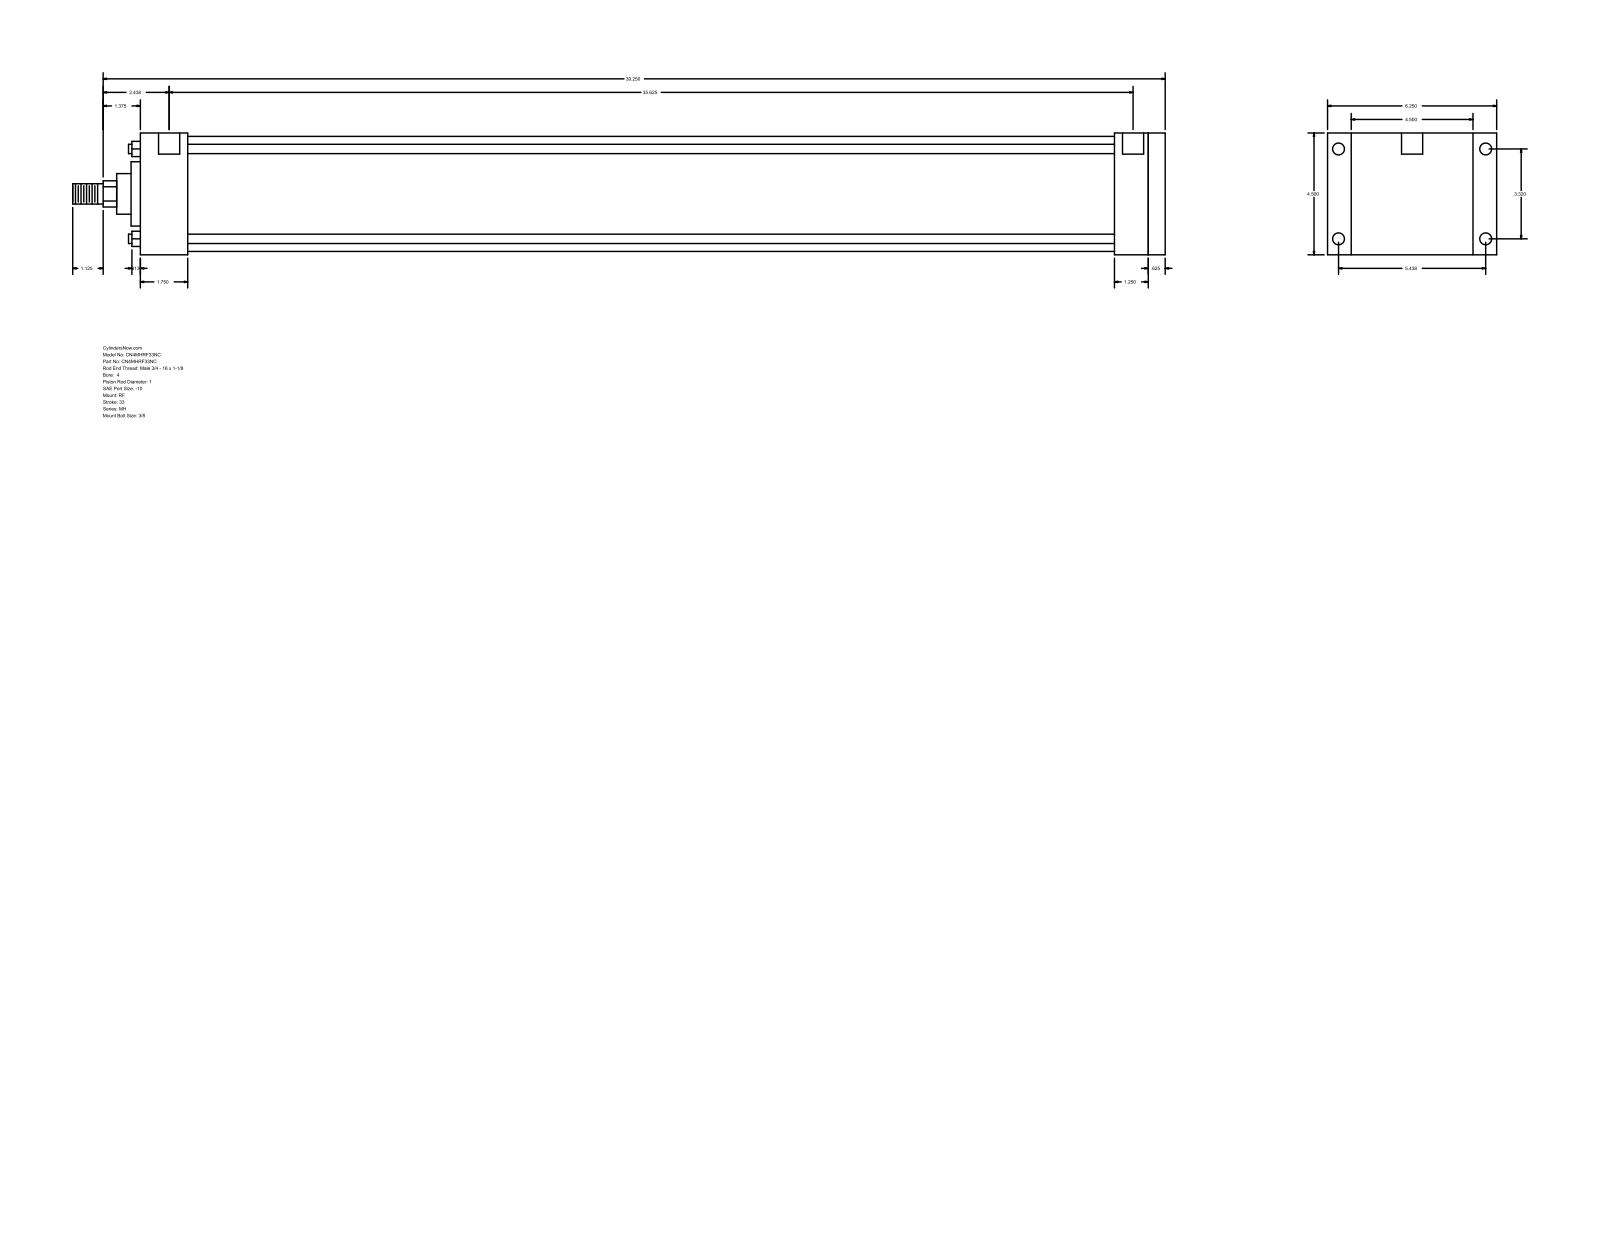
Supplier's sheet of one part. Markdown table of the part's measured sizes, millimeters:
| quantity | value |
| --- | --- |
| part name | MH_RF__0400_1 |
| STEP written by | GSSL Pune (CONFIG_CONTROL_DESIGN) |
| units | millimeters |
| bodies | 0 solids, 94 faces (65 planar, 29 cylindrical, 0 other) |
| overall size | 1025.53 × 158.75 × 114.3 |
| round holes (diameter × count) | 8.73 × 4, 11.13 × 4, 19.84 × 2 |
| round bosses / shafts (diameter × count) | 8.76 × 4, 107.95 × 1, 60.33 × 1, 38.1 × 1, 25.4 × 1, 19.05 × 1 |
| partial cylindrical surfaces (radius × count) | 12.29 × 1 |
| main face-to-face distances | 114.3, 962.03, 946.16, 15.87, 44.46, 901.7, 917.57, 914.41, 869.95, 31.75 |
| hole center spacings | 84.32, 138.12, 161.82, 908.05, 1.58, 1.59, 904.88, 906.46 |
